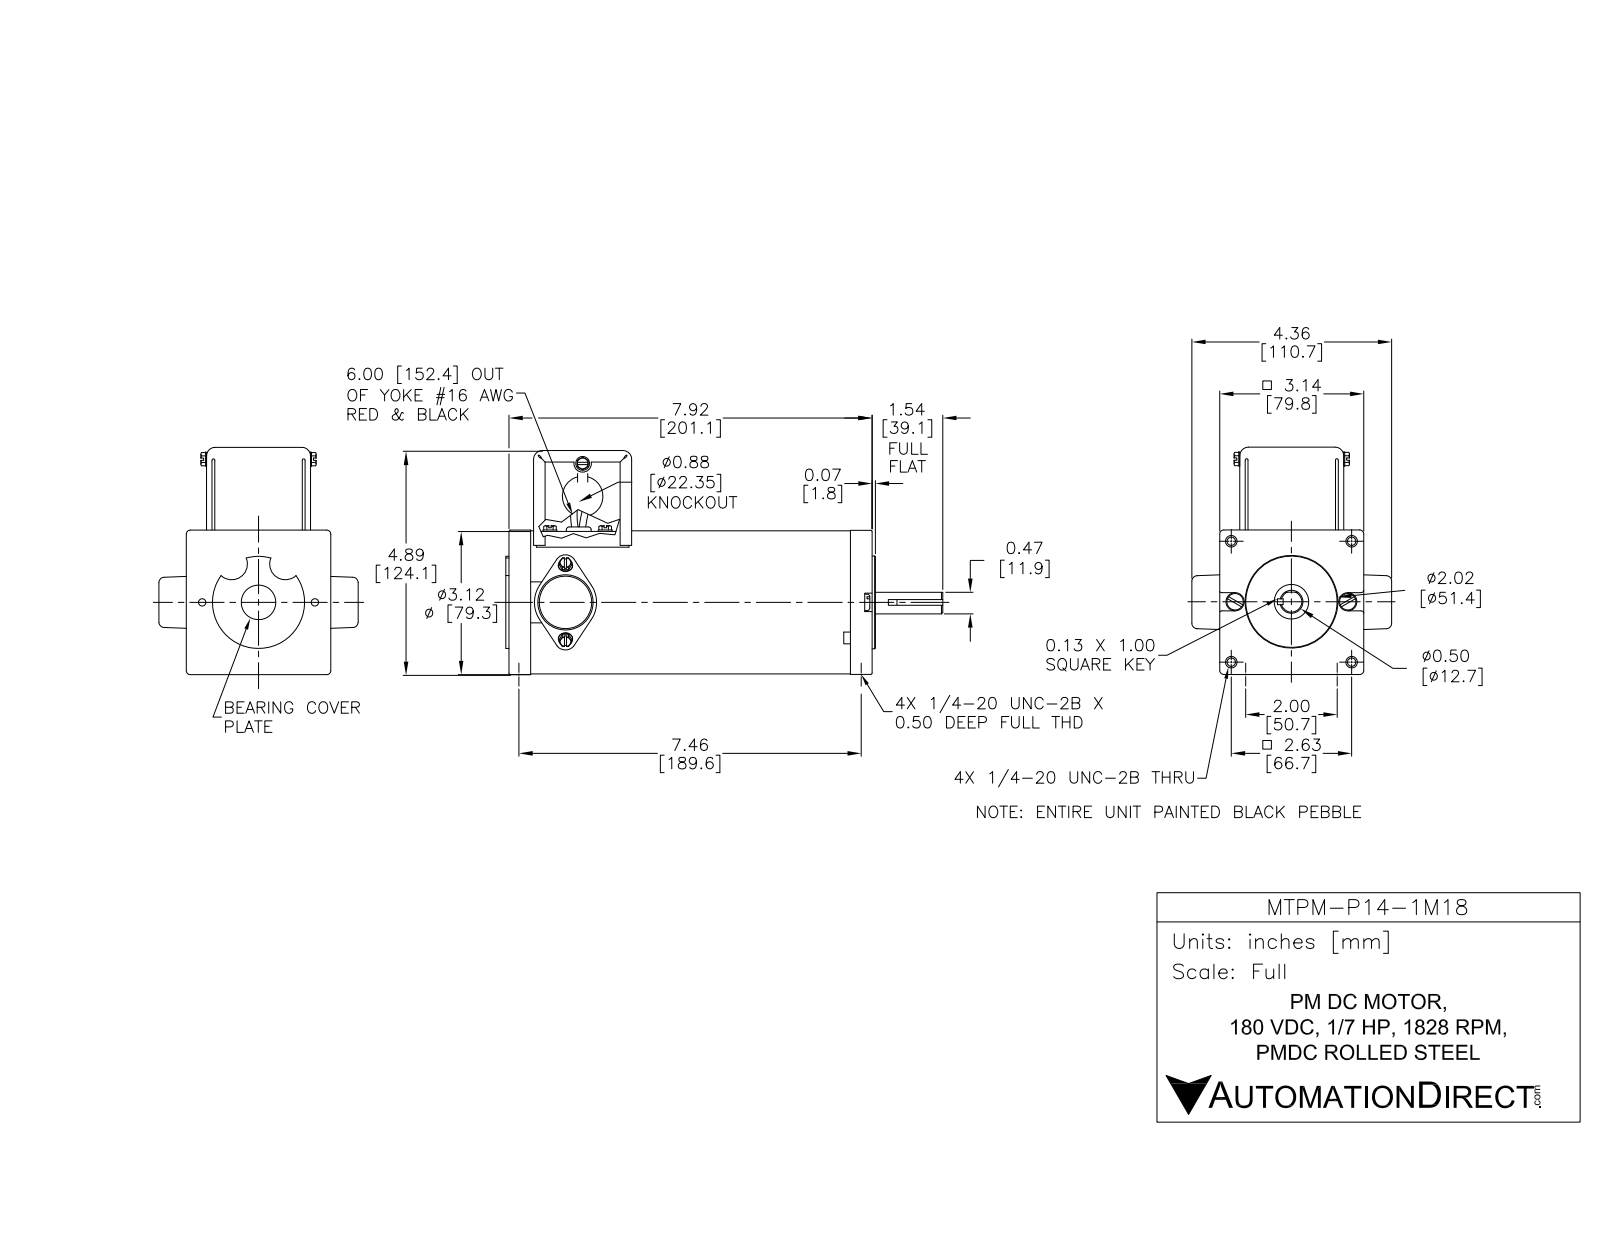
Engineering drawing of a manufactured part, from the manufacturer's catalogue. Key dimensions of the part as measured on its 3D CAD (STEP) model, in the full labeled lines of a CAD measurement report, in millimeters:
Part name (STEP PRODUCT): MTPM-P14-1M18
STEP written by: SolidWorks 2017 (AUTOMOTIVE_DESIGN)
Units: millimetres
Bodies: 28 solids, 409 faces (272 planar, 112 cylindrical, 25 other)
Overall size (bounding box): 241.8 × 125.6 × 111.5
Volume: 237 900 mm³ · Surface area: 188 100 mm²
Round holes (diameter × count): ⌀3.2 ×4, ⌀5 ×2, ⌀6.4 ×1, ⌀7.6 ×1, ⌀9.5 ×1, ⌀12.7 ×1, ⌀31.1 ×1, ⌀51.3 ×1, ⌀76.2 ×1, ⌀79.4 ×1
Round bosses / shafts (diameter × count): ⌀7.6 ×4, ⌀3.2 ×2, ⌀2.5 ×2, ⌀15.9 ×1, ⌀7.6 ×1
Partial cylindrical surfaces — rounded edges, fillets, slot ends (radius × count): R4.9 ×4, R5.9 ×4, R4 ×2, R8.7 ×2, R15.6 ×1, R16.9 ×1, R17.2 ×1, R25.4 ×1
Main face-to-face distances: 0.8, 6.4, 194.7, 1.6, 54.2, 188.3, 52, 2.4, 201, 55.8
Hole centre spacings: 33.5, 47.2, 66.8, 72.8, 31.2, 94.5, 62.5, 78.3
